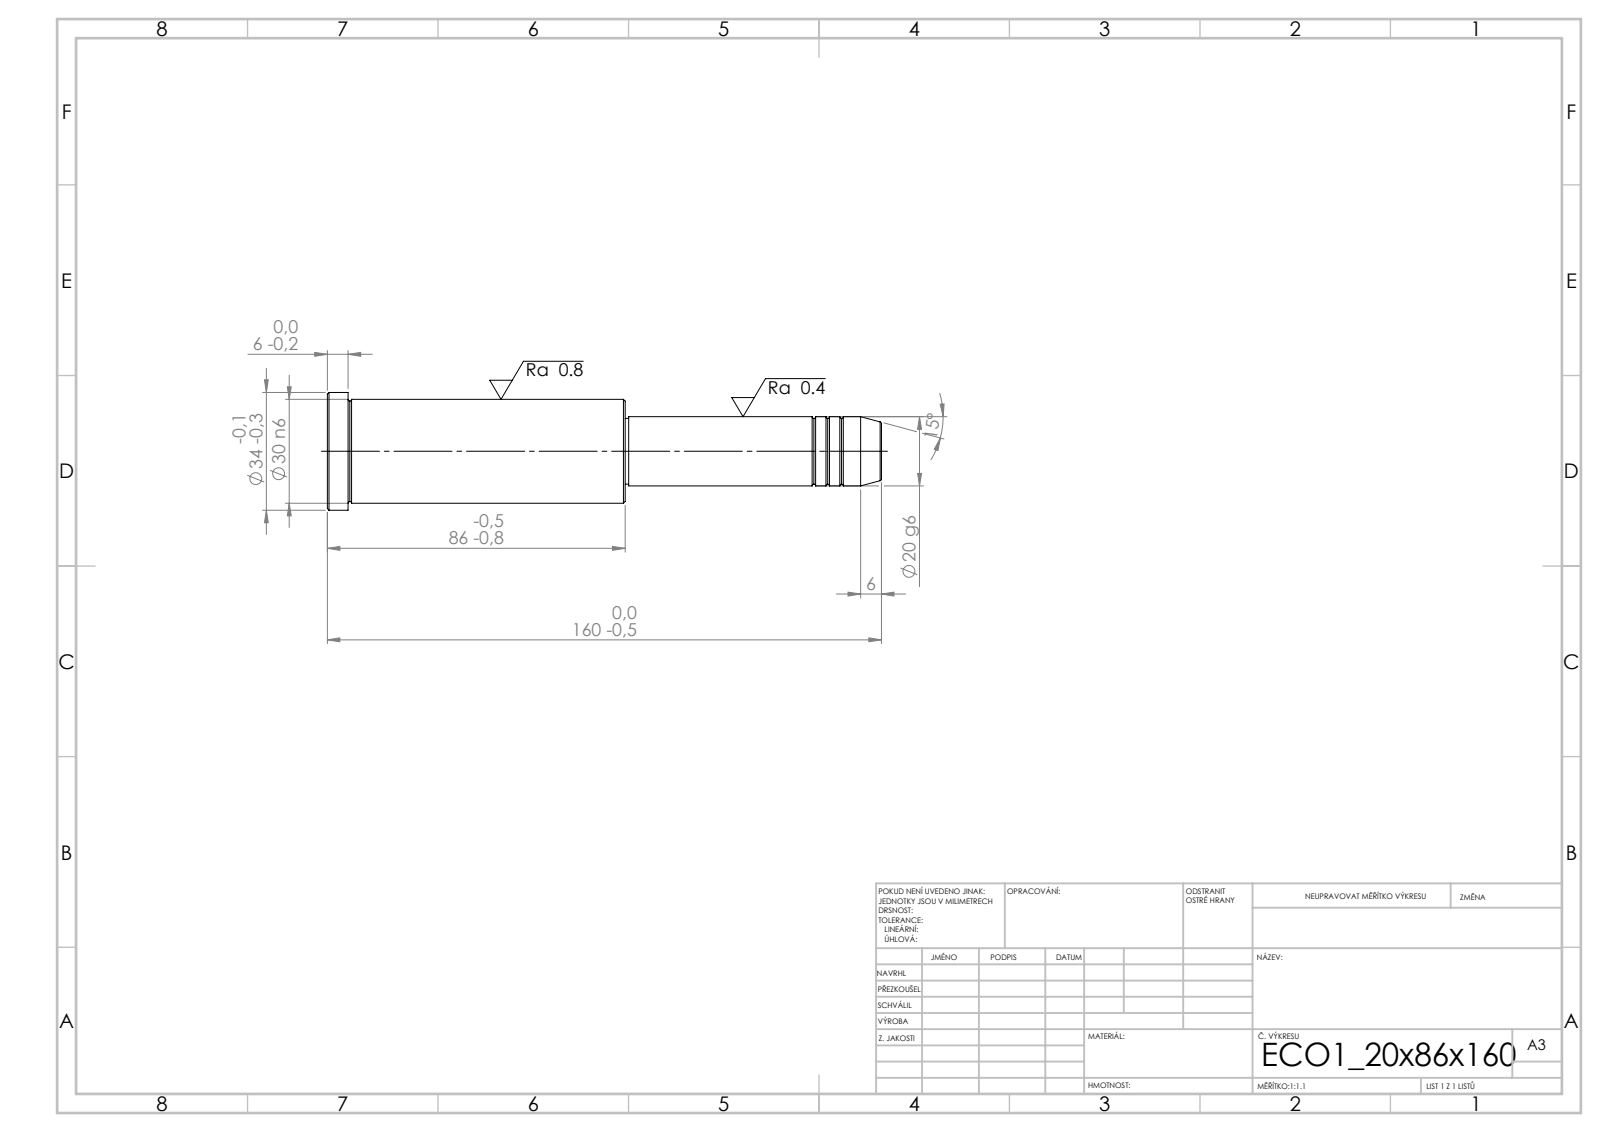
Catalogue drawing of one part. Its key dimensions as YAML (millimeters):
step_written_by: "SolidWorks 2019 (CONFIG_CONTROL_DESIGN)"
units: millimeters
bodies: {solids: 1, faces: 43, planar: 5, cylindrical: 14, other: 24}
overall_size: [160, 34, 34]
volume: 84791
surface_area: 14677
round_bosses_or_shafts:
  - {diameter: 34, count: 1}
  - {diameter: 30, count: 1}
  - {diameter: 20, count: 1}
  - {diameter: 19, count: 1}
face_to_face_distances: [86, 74, 160, 154, 80, 6, 73, 1, 81, 87]
